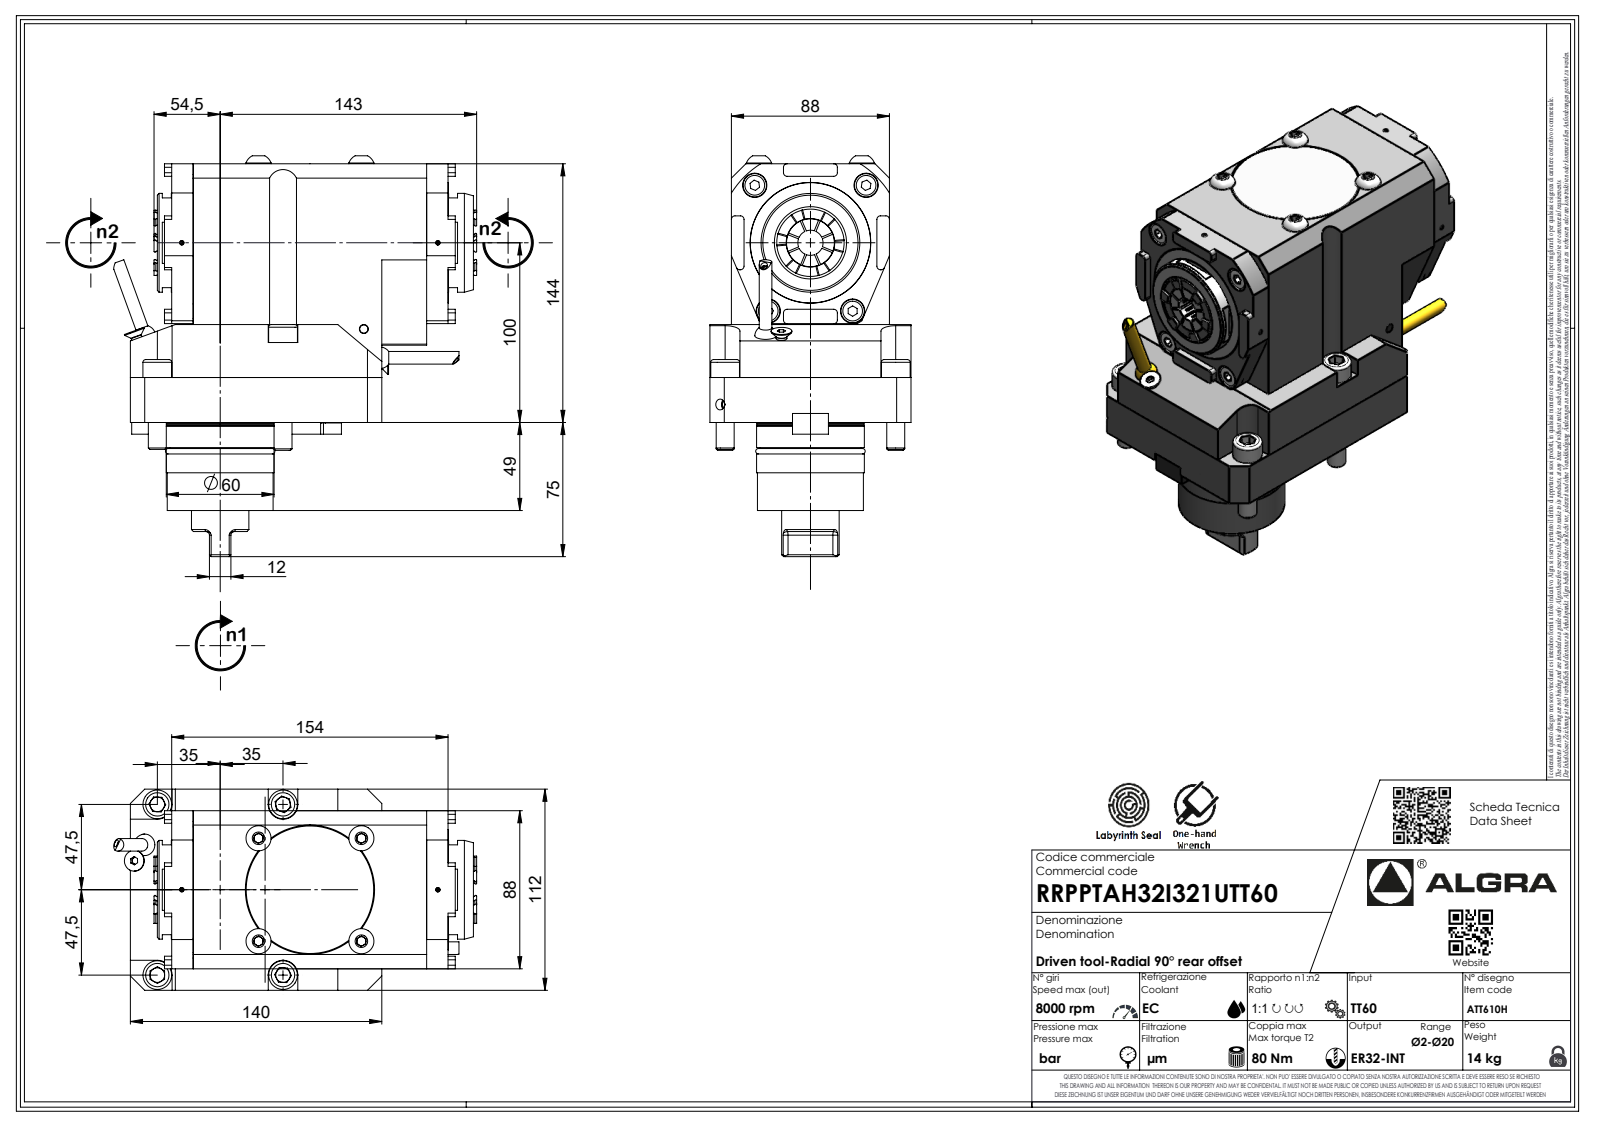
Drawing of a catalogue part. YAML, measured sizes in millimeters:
part_name: "RRPPTAH32I321UTT60"
step_written_by: "SolidWorks 2023 (AUTOMOTIVE_DESIGN)"
units: millimeters
bodies: {solids: 1, faces: 681, planar: 429, cylindrical: 126, other: 126}
overall_size: [223.1, 200.26, 112]
volume: 2215000
surface_area: 138384
round_holes:
  - {diameter: 4, count: 2}
  - {diameter: 2.1, count: 1}
  - {diameter: 6, count: 1}
round_bosses_or_shafts:
  - {diameter: 16, count: 4}
  - {diameter: 14, count: 4}
  - {diameter: 10, count: 4}
  - {diameter: 7, count: 2}
  - {diameter: 74, count: 1}
  - {diameter: 67, count: 1}
  - {diameter: 60, count: 1}
  - {diameter: 59.6, count: 1}
partial_cylinders:
  - {radius: 2, count: 26}
  - {radius: 0.33, count: 7}
  - {radius: 0.52, count: 7}
  - {radius: 3.7, count: 7}
  - {radius: 8.25, count: 4}
  - {radius: 1, count: 2}
  - {radius: 4.5, count: 2}
  - {radius: 5, count: 2}
face_to_face_distances: [12, 100, 144, 88, 112, 142, 35, 140, 117, 23]
